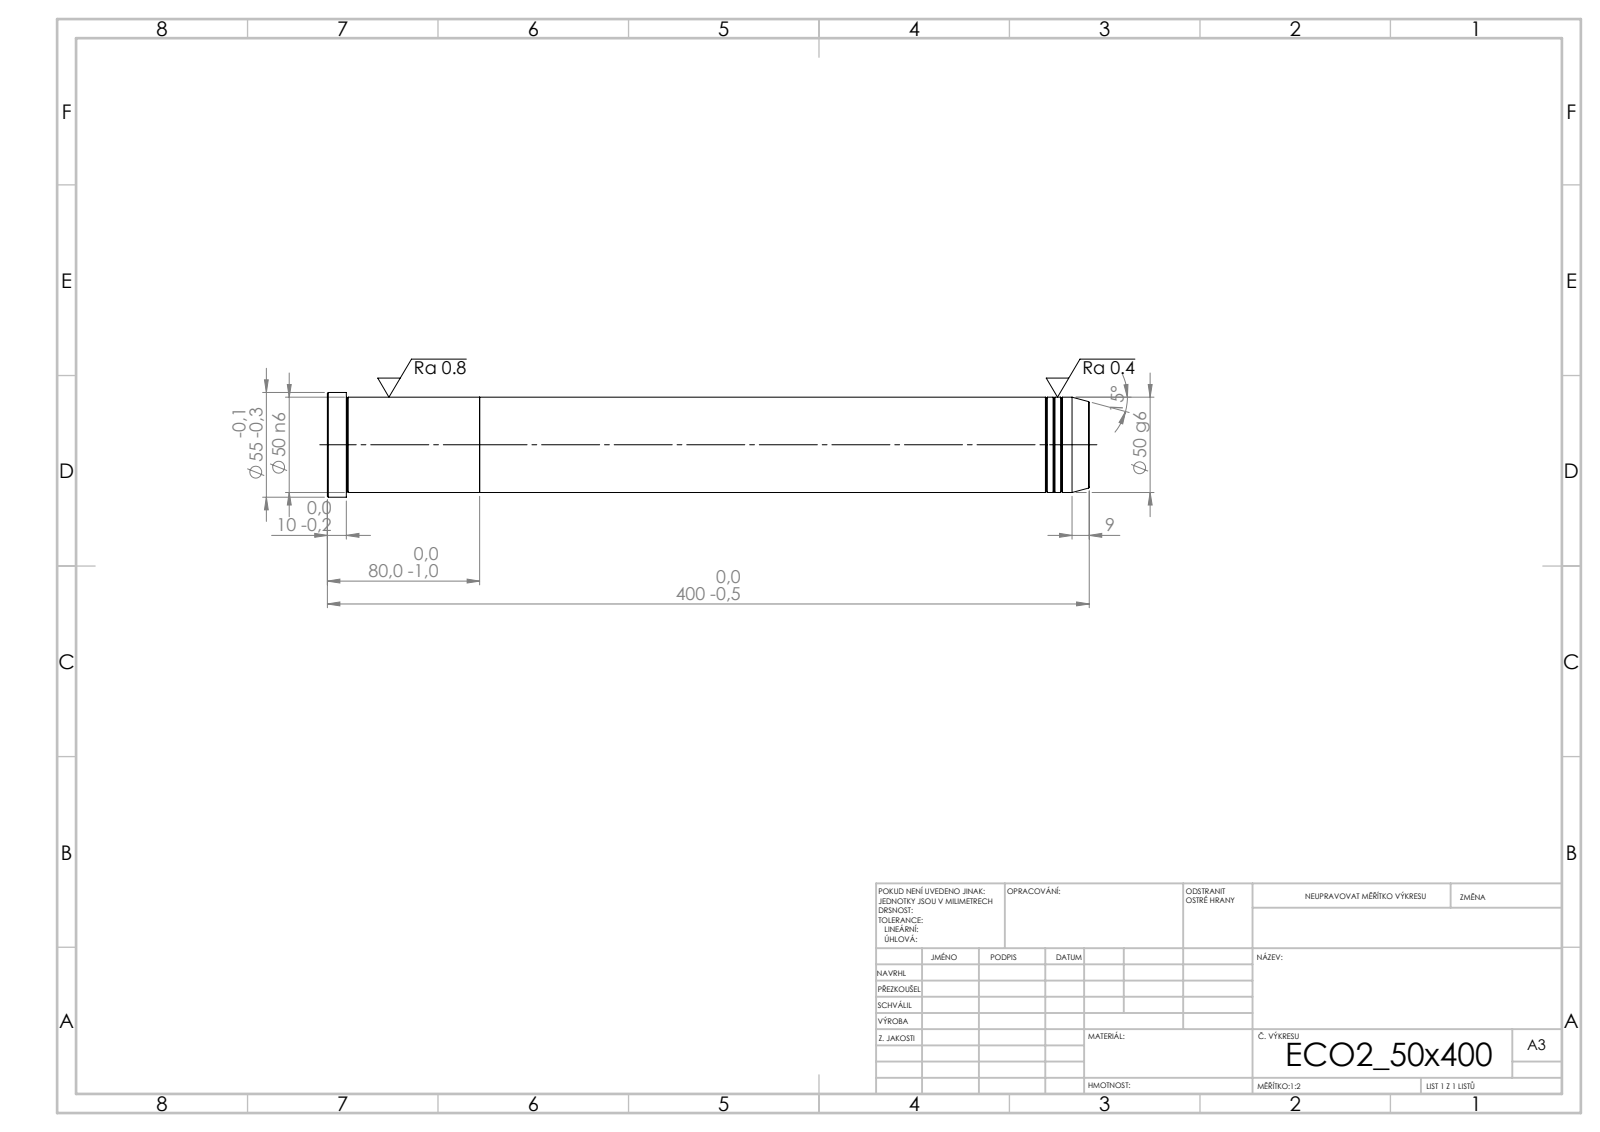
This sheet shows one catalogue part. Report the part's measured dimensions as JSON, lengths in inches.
{"step_written_by": "SolidWorks 2019 (CONFIG_CONTROL_DESIGN)", "units": "inches", "bodies": {"solids": 2, "faces": 39, "planar": 5, "cylindrical": 12, "other": 22}, "overall_size": [15.748, 2.165, 2.165], "volume_in3": 48.06, "surface_area_in2": 110.9, "round_bosses_or_shafts": [[2.165, 1], [1.969, 1]], "face_to_face_distances": [3.15, 12.598, 15.748, 15.354, 2.756, 0.394]}
